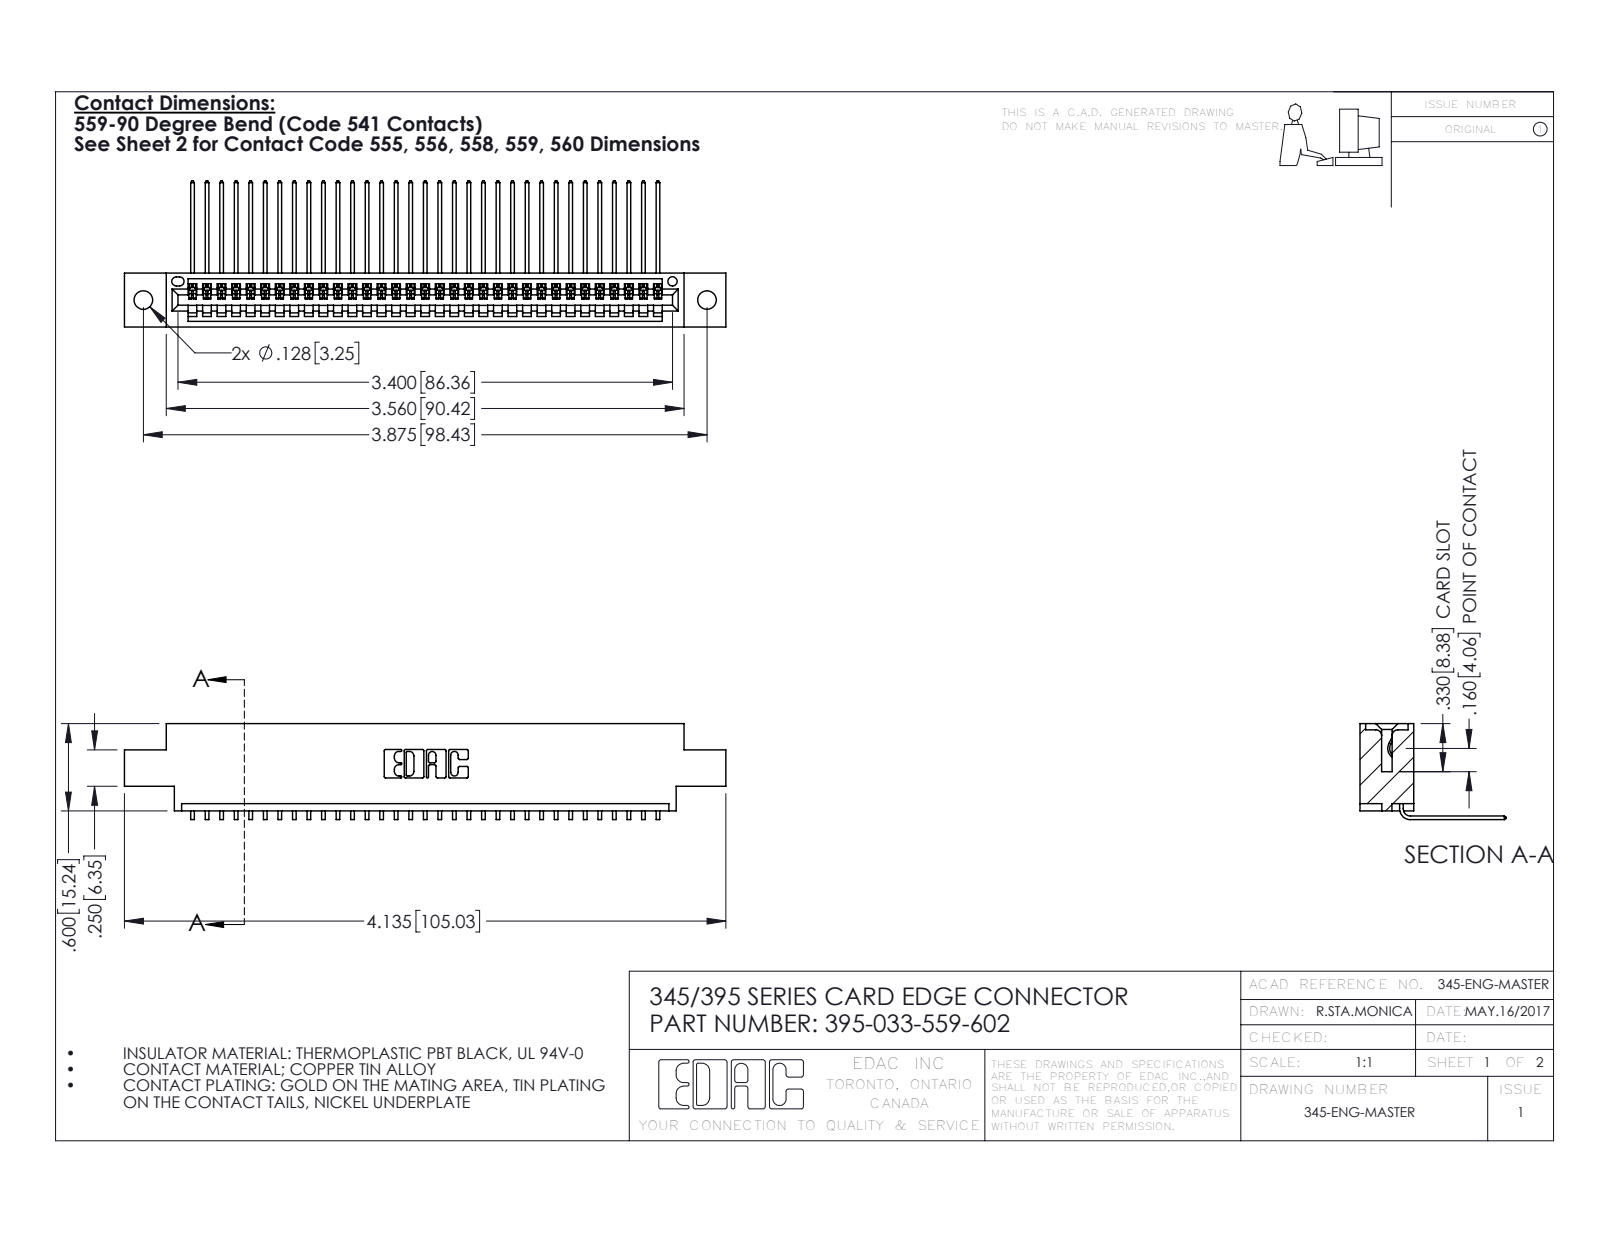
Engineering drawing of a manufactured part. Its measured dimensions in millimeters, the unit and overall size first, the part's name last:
Units: millimetres
Overall size (bounding box): 105 × 25.5 × 16.7
Round holes (diameter × count): ⌀3.3 ×2, ⌀1.6 ×1
Partial cylindrical surfaces — rounded edges, fillets, slot ends (radius × count): R0.2 ×66, R0.3 ×22, R0.2 ×6, R0.8 ×6, R0.7 ×3, R0.8 ×2, R1 ×2, R0.4 ×1
Main face-to-face distances: 1.8, 7.6, 9.4, 5.1, 2.5, 6.9, 0.6, 5.7, 4.4, 3.8
Hole centre spacings: 6.9, 92.5, 98.4
Volume: 9 870 mm³ · Surface area: 13 480 mm²
Bodies: 34 solids, 2110 faces (1470 planar, 640 cylindrical, 0 other)
Part name (STEP PRODUCT): 395-033-559-602; 345-292-001_558 559 Tail - 1; 345 Part_0.170 Offset - 0.128 Dia
STEP written by: SolidWorks 2016 (CONFIG_CONTROL_DESIGN)
